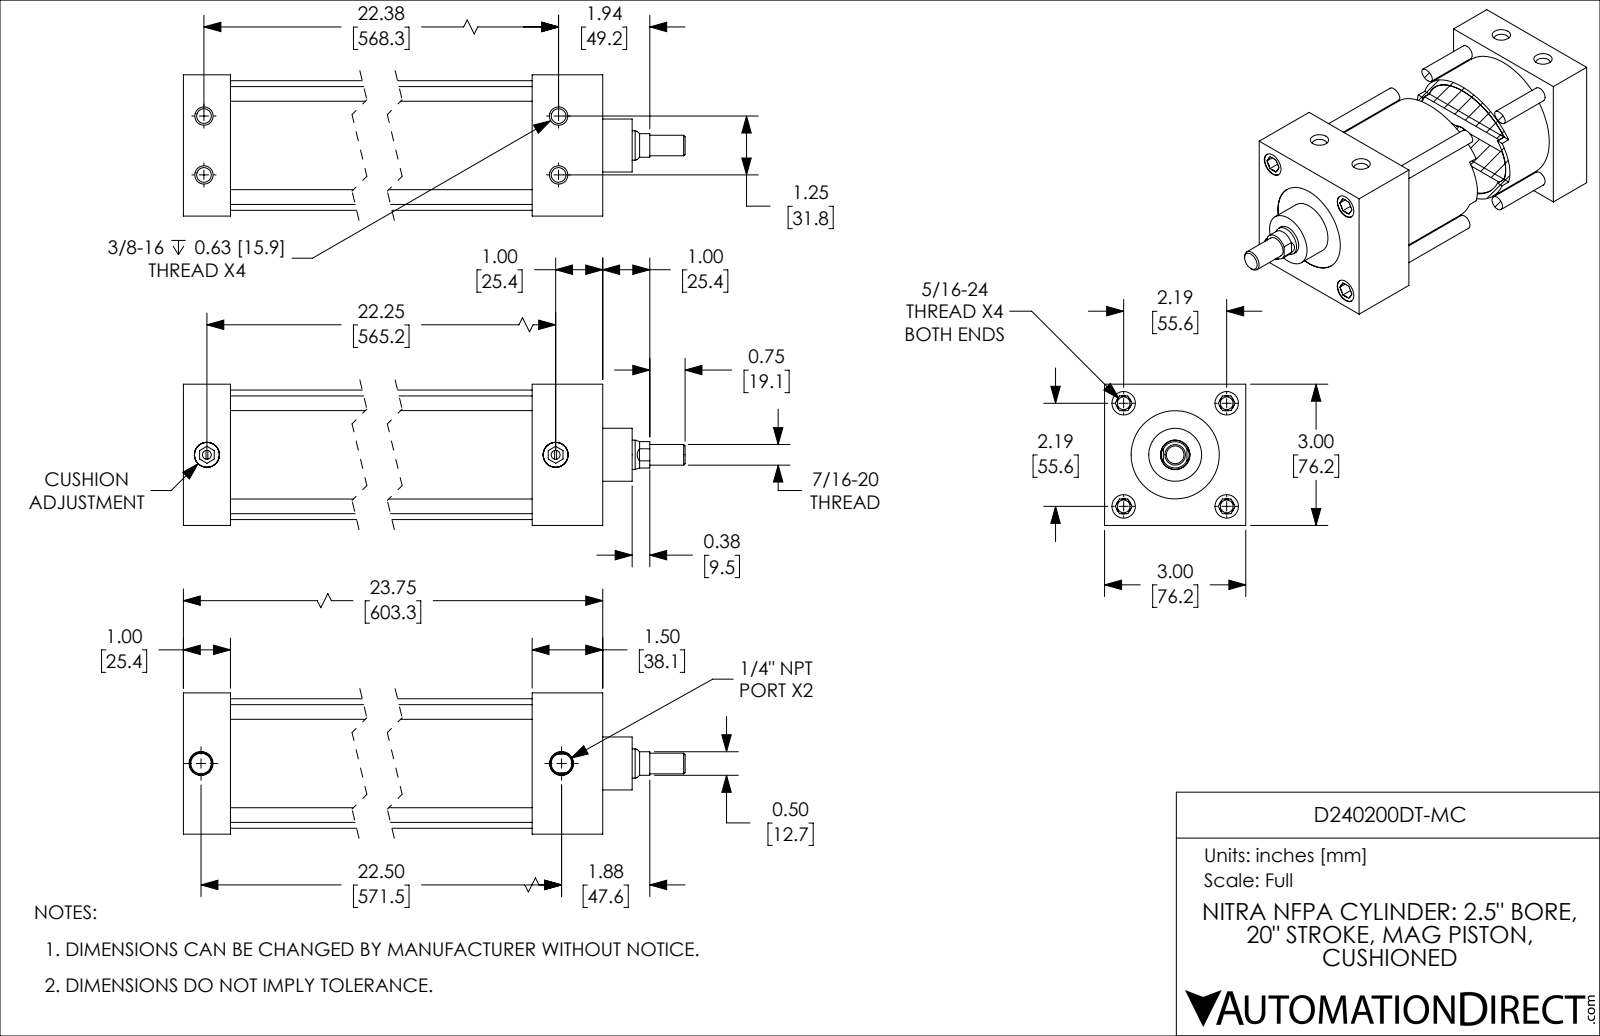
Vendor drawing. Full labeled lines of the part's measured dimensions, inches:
Part name (STEP PRODUCT): D240200DT-MC_PISTON_KK1; D240200DT-MC; D240200DT-MC_CUSHION; D240200DT-MC_BODY
STEP written by: SolidWorks 2019 (CONFIG_CONTROL_DESIGN)
Units: inches
Bodies: 4 solids, 248 faces (90 planar, 78 cylindrical, 80 other)
Overall size (bounding box): 25.5 × 3 × 3
Volume: 62.86 in³ · Surface area: 581.8 in²
Round holes (diameter × count): ⌀0.272 ×4, ⌀0.313 ×4, ⌀0.5 ×4, ⌀0.19 ×2, ⌀0.438 ×2, ⌀0.531 ×2, ⌀0.626 ×1, ⌀1.875 ×1, ⌀2.501 ×1
Round bosses / shafts (diameter × count): ⌀0.312 ×4, ⌀0.532 ×2, ⌀2.751 ×1, ⌀2.499 ×1, ⌀1.125 ×1, ⌀0.624 ×1, ⌀0.437 ×1
Partial cylindrical surfaces — rounded edges, fillets, slot ends (radius × count): R0.281 ×1
Main face-to-face distances: 3, 1, 22.25, 21.25, 23.75, 22.75, 1.5, 1.25, 2.25, 20
Hole centre spacings: 1.548, 2.19, 22.446, 0.628, 0.628, 1.25, 3.097, 22.375
